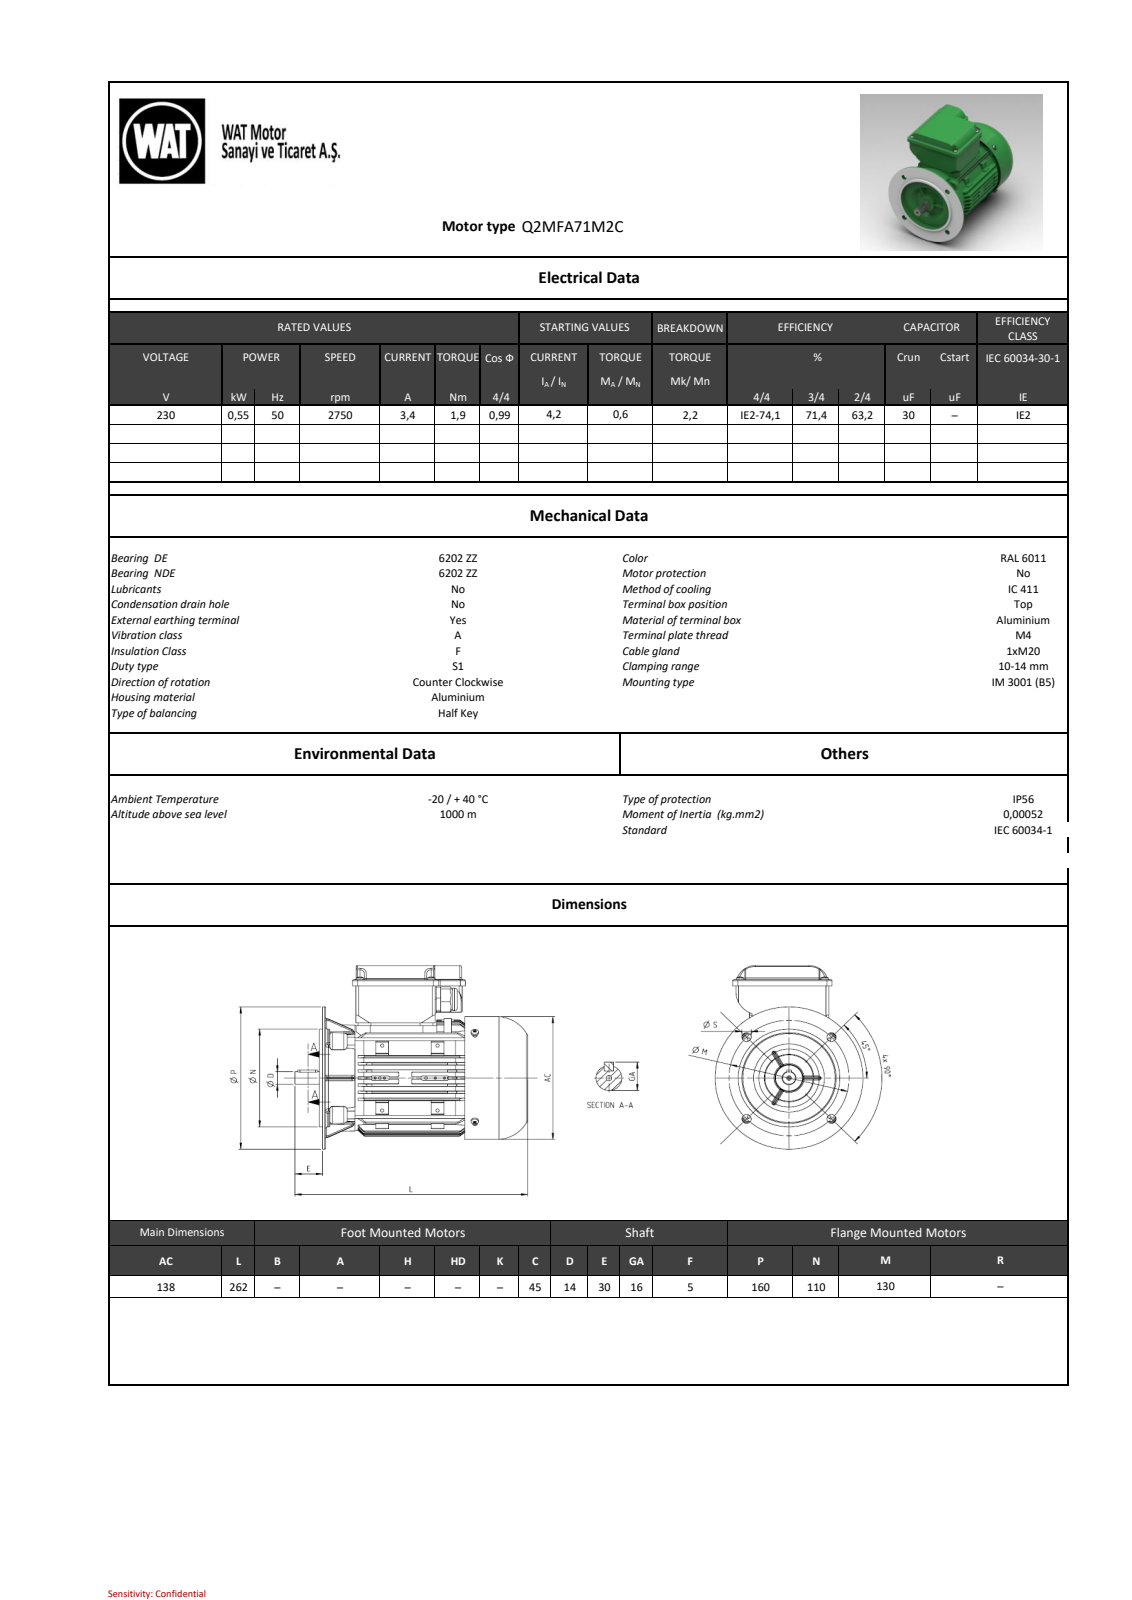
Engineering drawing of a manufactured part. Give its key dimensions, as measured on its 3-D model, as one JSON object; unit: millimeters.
{"part_name": "BY6434017xx_004-TK_QM63-80; BY6424130xx_004-TKK_QM63-80; BY6432282xx_005-MOTOR_KAPAGI_QS71FA_ISLEME_YENI; 641304741_AZ-KAMA PARALEL A 5x5x22 St50 DIN6885 (+6 more)", "step_written_by": "SIEMENS PLM Software NX2206.8101 (AUTOMOTIVE_DESIGN)", "units": "millimeters", "bodies": {"solids": 24, "faces": 2910, "planar": 1252, "cylindrical": 785, "other": 873}, "overall_size": [262, 206.5, 160], "volume_mm3": 763556, "surface_area_mm2": 498645, "round_holes": [[3.3, 9], [3.65, 8], [4.5, 8], [2.5, 6], [4, 4], [4.65, 4], [4.8, 4], [10, 4], [3, 3], [3.7, 3], [4.6, 2], [5, 1]], "round_bosses_or_shafts": [[8, 8], [4, 8], [3, 8], [160, 1], [138, 1], [110, 1], [26, 1], [25.28, 1]], "partial_cylinders_radius": [[1, 141], [2, 66], [1.2, 36], [0.5, 32], [10, 32], [0.75, 18], [5, 18], [2.5, 14]], "face_to_face_distances": [3, 194.5, 2, 5, 158.5, 189.2, 194.2, 197.5, 3.5, 36], "hole_center_spacings": [87.43, 89.67, 89.74, 55, 36.59, 65, 60, 3.13]}
